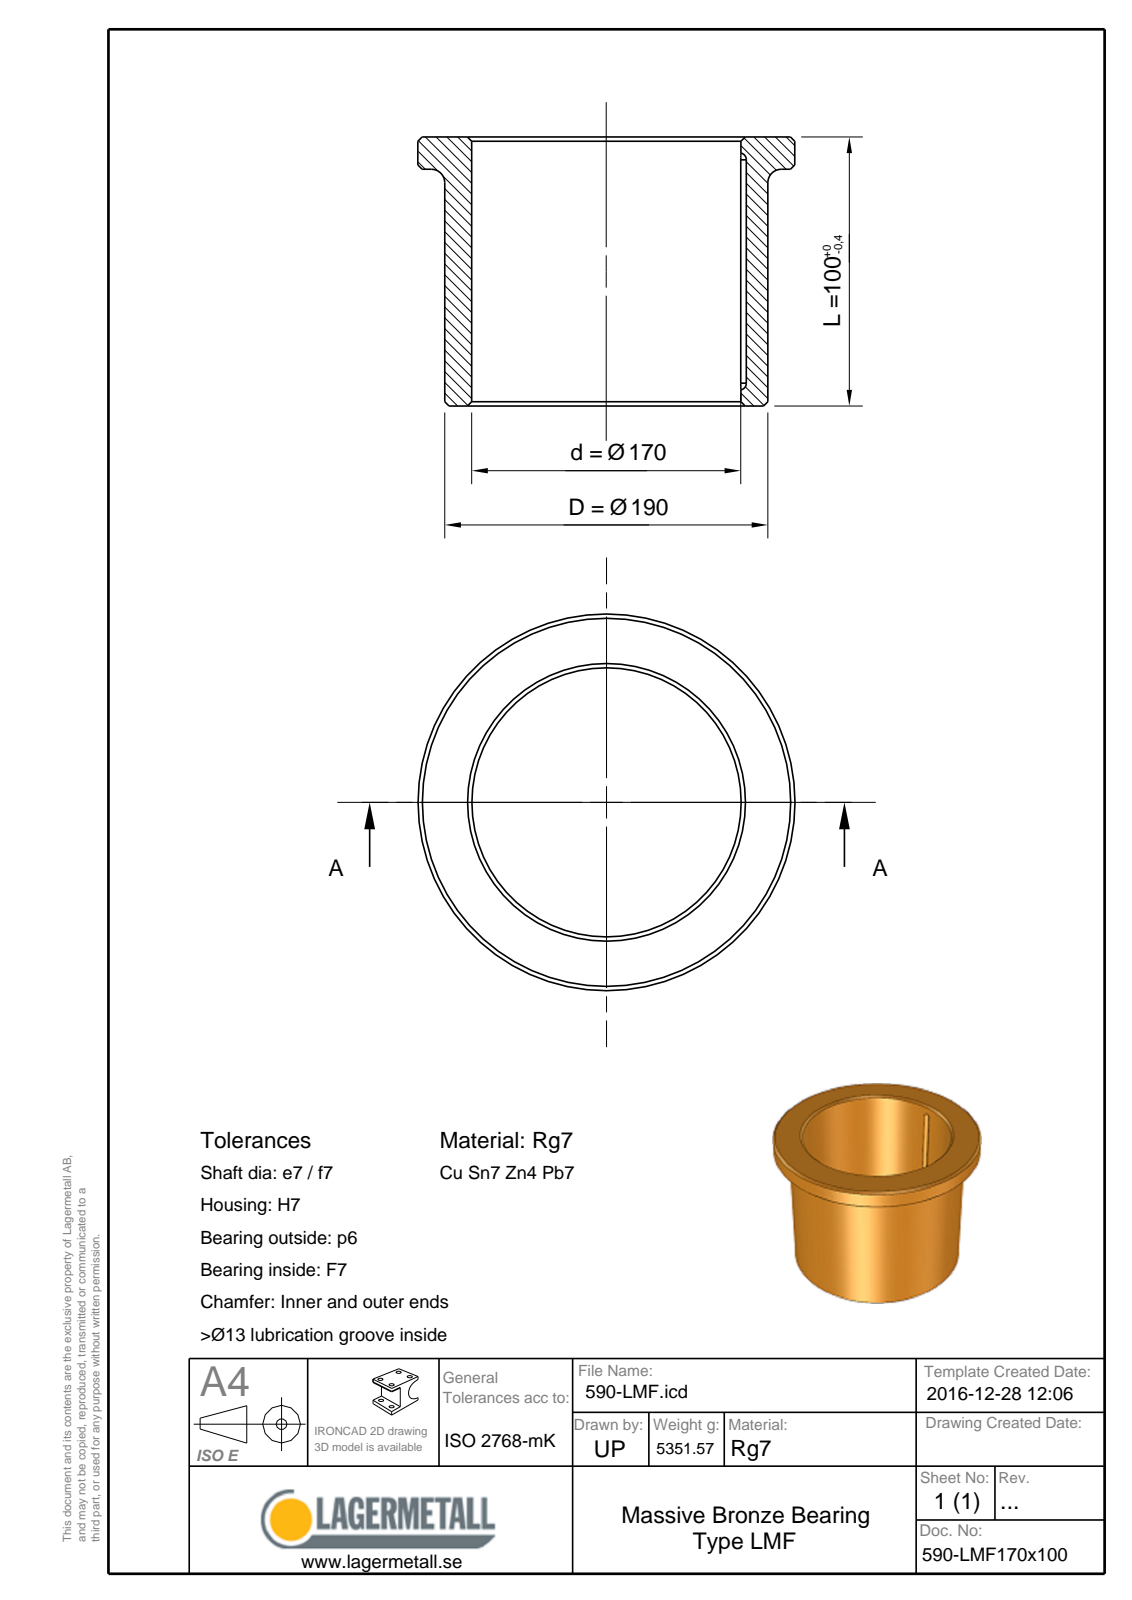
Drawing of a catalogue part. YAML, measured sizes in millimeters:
part_name: "590-LMF170x100"
step_written_by: "Spatial InterOp 3D (CONFIG_CONTROL_DESIGN)"
units: millimeters
bodies: {solids: 1, faces: 17, planar: 4, cylindrical: 5, other: 8}
overall_size: [205, 205, 100]
volume: 608139
surface_area: 129773
round_holes:
  - {diameter: 170, count: 1}
round_bosses_or_shafts:
  - {diameter: 205, count: 1}
  - {diameter: 190, count: 1}
partial_cylinders:
  - {radius: 2.25, count: 2}
face_to_face_distances: [100, 90, 10]
